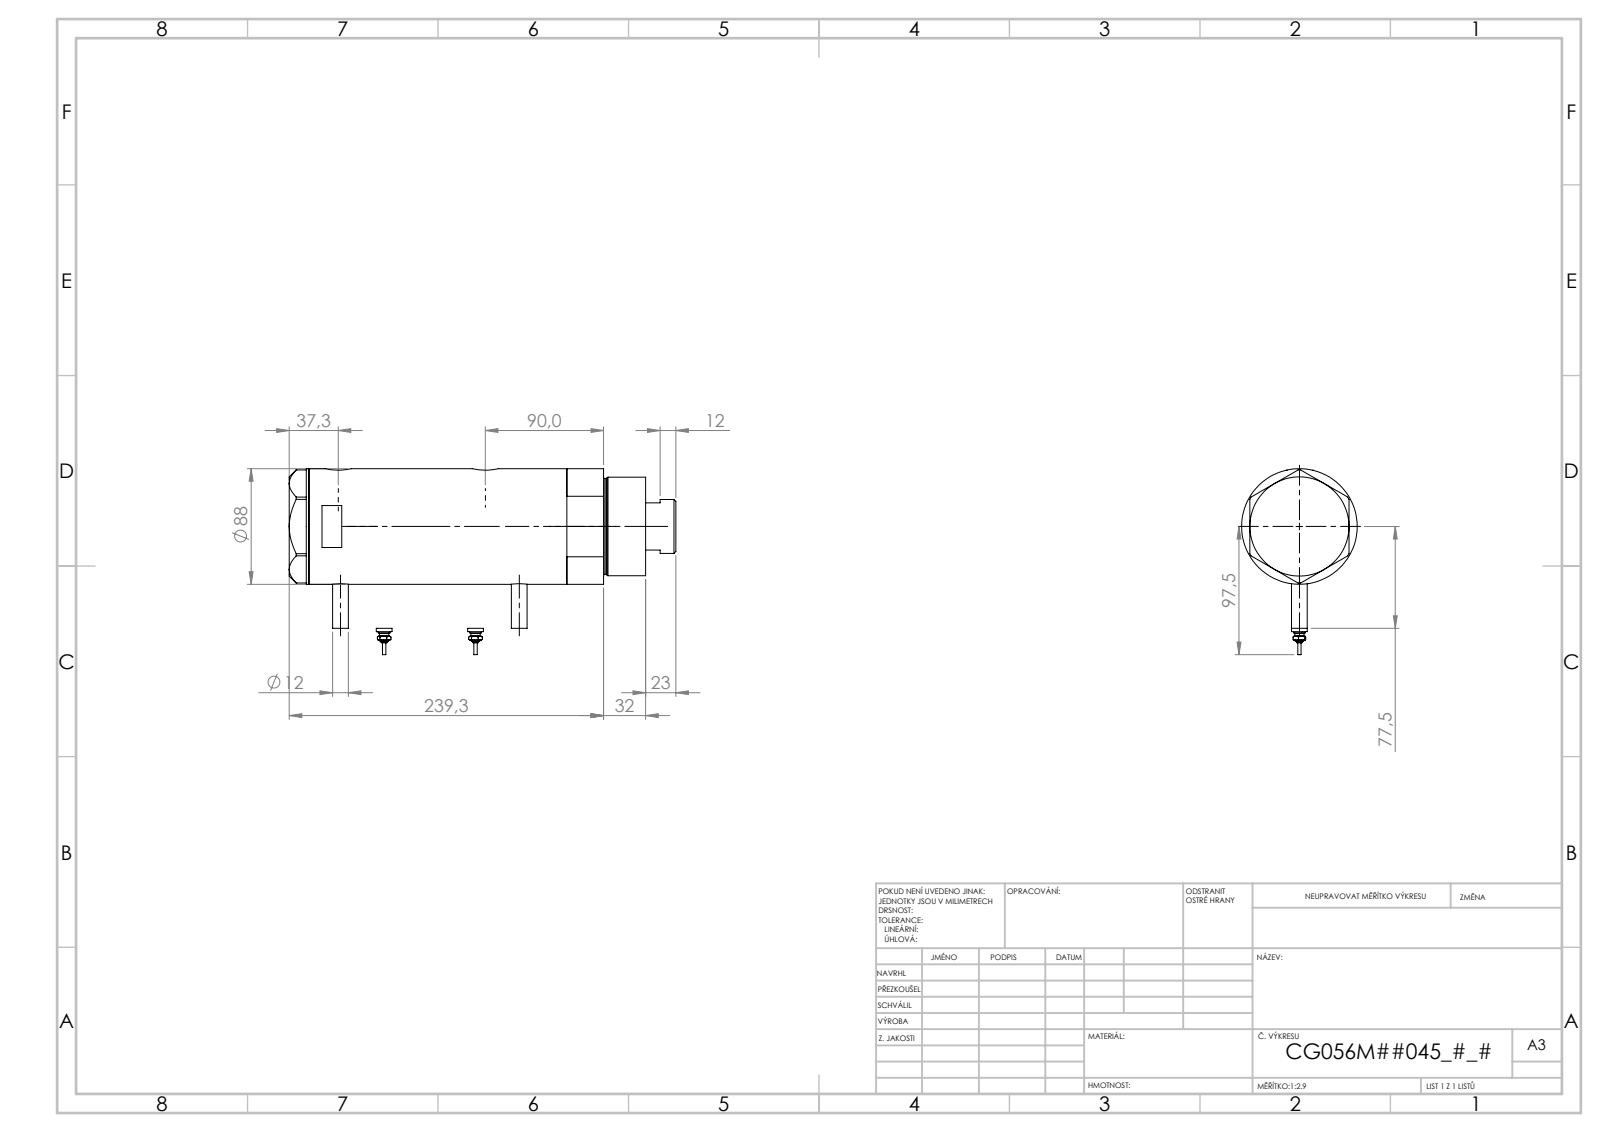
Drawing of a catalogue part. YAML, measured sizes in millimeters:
part_name: "V270CG_SWITCH; V270CG_FRONT; V270CG_MIDDLE; V270CG_VC (+1 more)"
step_written_by: "SolidWorks 2019 (CONFIG_CONTROL_DESIGN)"
units: millimeters
bodies: {solids: 6, faces: 232, planar: 81, cylindrical: 77, other: 74}
overall_size: [269.47, 120.3, 88]
volume: 1390000
surface_area: 208502
round_holes:
  - {diameter: 5, count: 2}
  - {diameter: 12.5, count: 2}
  - {diameter: 13.16, count: 2}
  - {diameter: 20, count: 2}
  - {diameter: 14.5, count: 1}
  - {diameter: 42, count: 1}
  - {diameter: 43.5, count: 1}
  - {diameter: 56, count: 1}
  - {diameter: 60, count: 1}
  - {diameter: 80, count: 1}
round_bosses_or_shafts:
  - {diameter: 12, count: 2}
  - {diameter: 9, count: 2}
  - {diameter: 7, count: 2}
  - {diameter: 4.34, count: 2}
  - {diameter: 2.4, count: 2}
  - {diameter: 88, count: 1}
  - {diameter: 75, count: 1}
  - {diameter: 73, count: 1}
face_to_face_distances: [119.4, 26, 93.4, 15, 41, 134.4, 231.47, 246.47, 205.47, 112.07]
hole_center_spacings: [1.7, 25.8, 95.3, 97, 121.1, 122.8]
